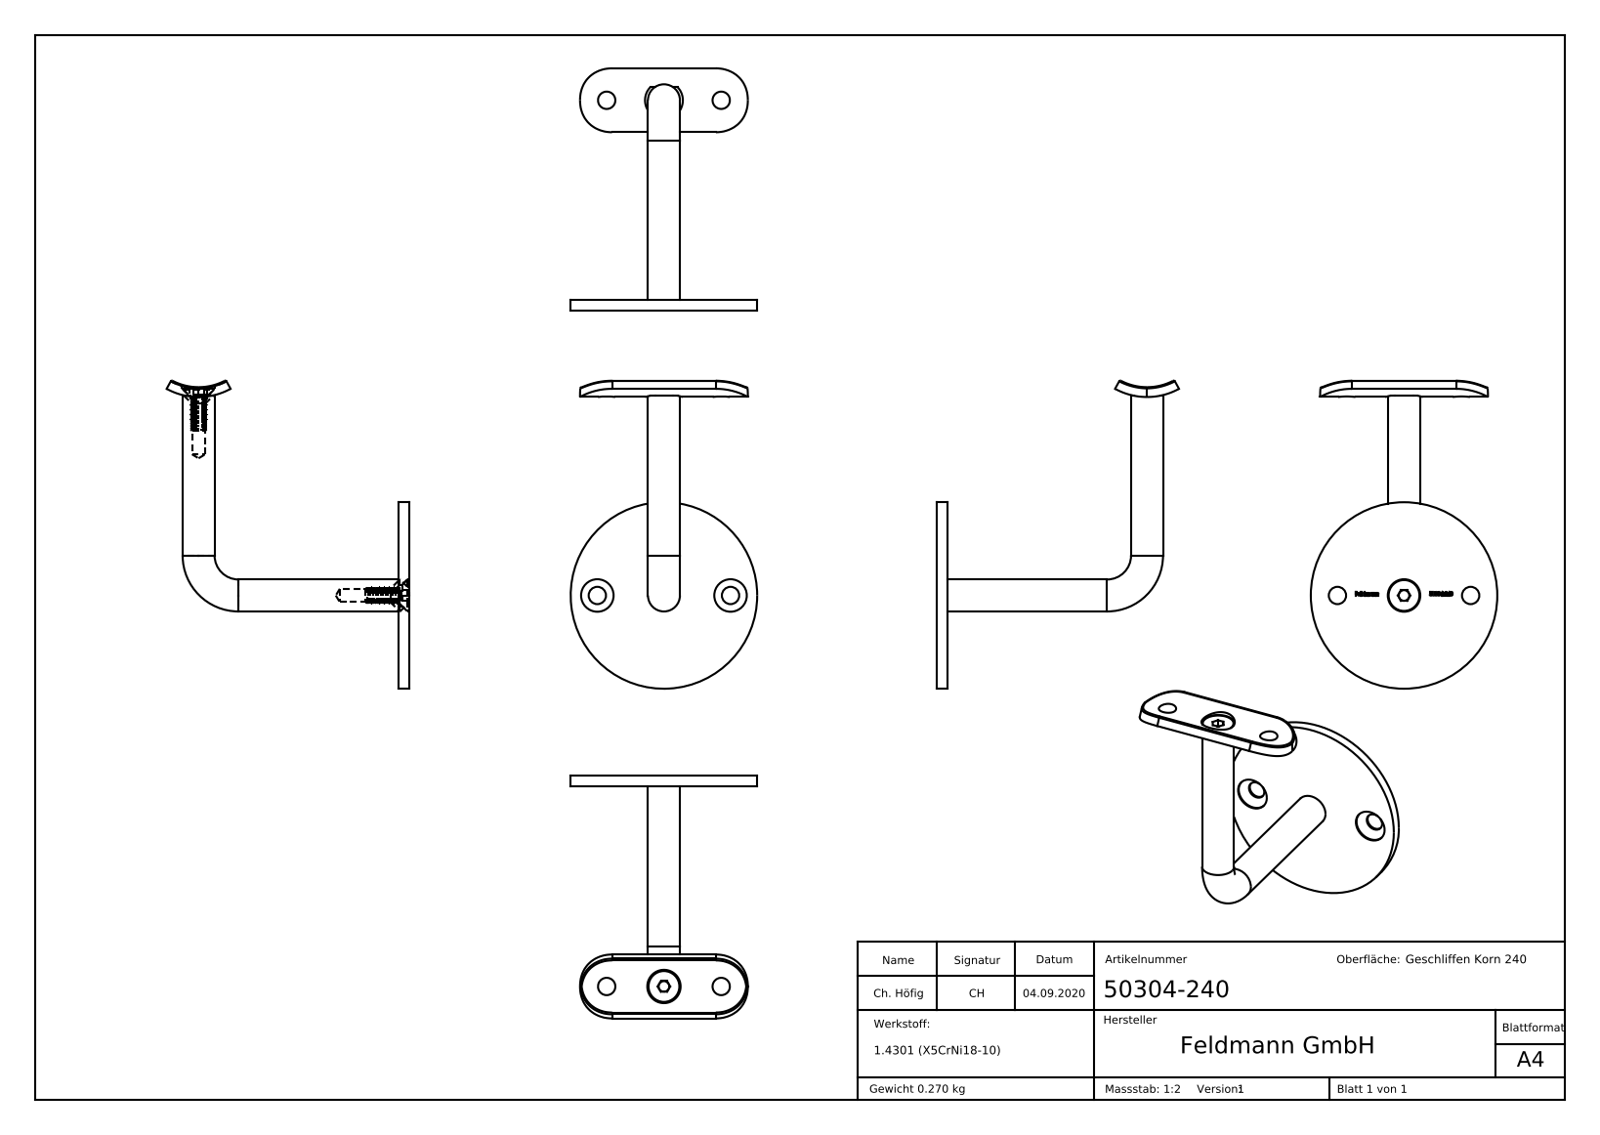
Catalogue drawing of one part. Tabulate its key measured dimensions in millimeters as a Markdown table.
| quantity | value |
| --- | --- |
| part name | 50304-240; 50304-240 Teil2; 50304-240 Teil2_50304-240 Teil 2; 50304-240 Teil3_50304-240 Teil3 (+5 more) |
| STEP written by | SolidWorks 2018 (CONFIG_CONTROL_DESIGN) |
| units | millimeters |
| bodies | 5 solids, 489 faces (159 planar, 93 cylindrical, 237 other) |
| overall size | 115.65 × 91 × 70 |
| volume | 35 029 mm³ |
| surface area | 19 345 mm² |
| round holes (diameter × count) | 6.5 × 4, 12.2 × 3, 5 × 2, 8 × 2, 12.5 × 1 |
| round bosses / shafts (diameter × count) | 12 × 2, 11.57 × 2, 6 × 2, 70 × 1 |
| partial cylindrical surfaces (radius × count) | 12 × 4, 0.5 × 2, 7.1 × 1, 21.2 × 1, 24.9 × 1 |
| main face-to-face distances | 4, 2.8, 3.7, 16, 4.02, 16.3, 12.3, 13.2, 72.99, 77.01 |
| hole center spacings | 21.5, 25, 43, 50 |
